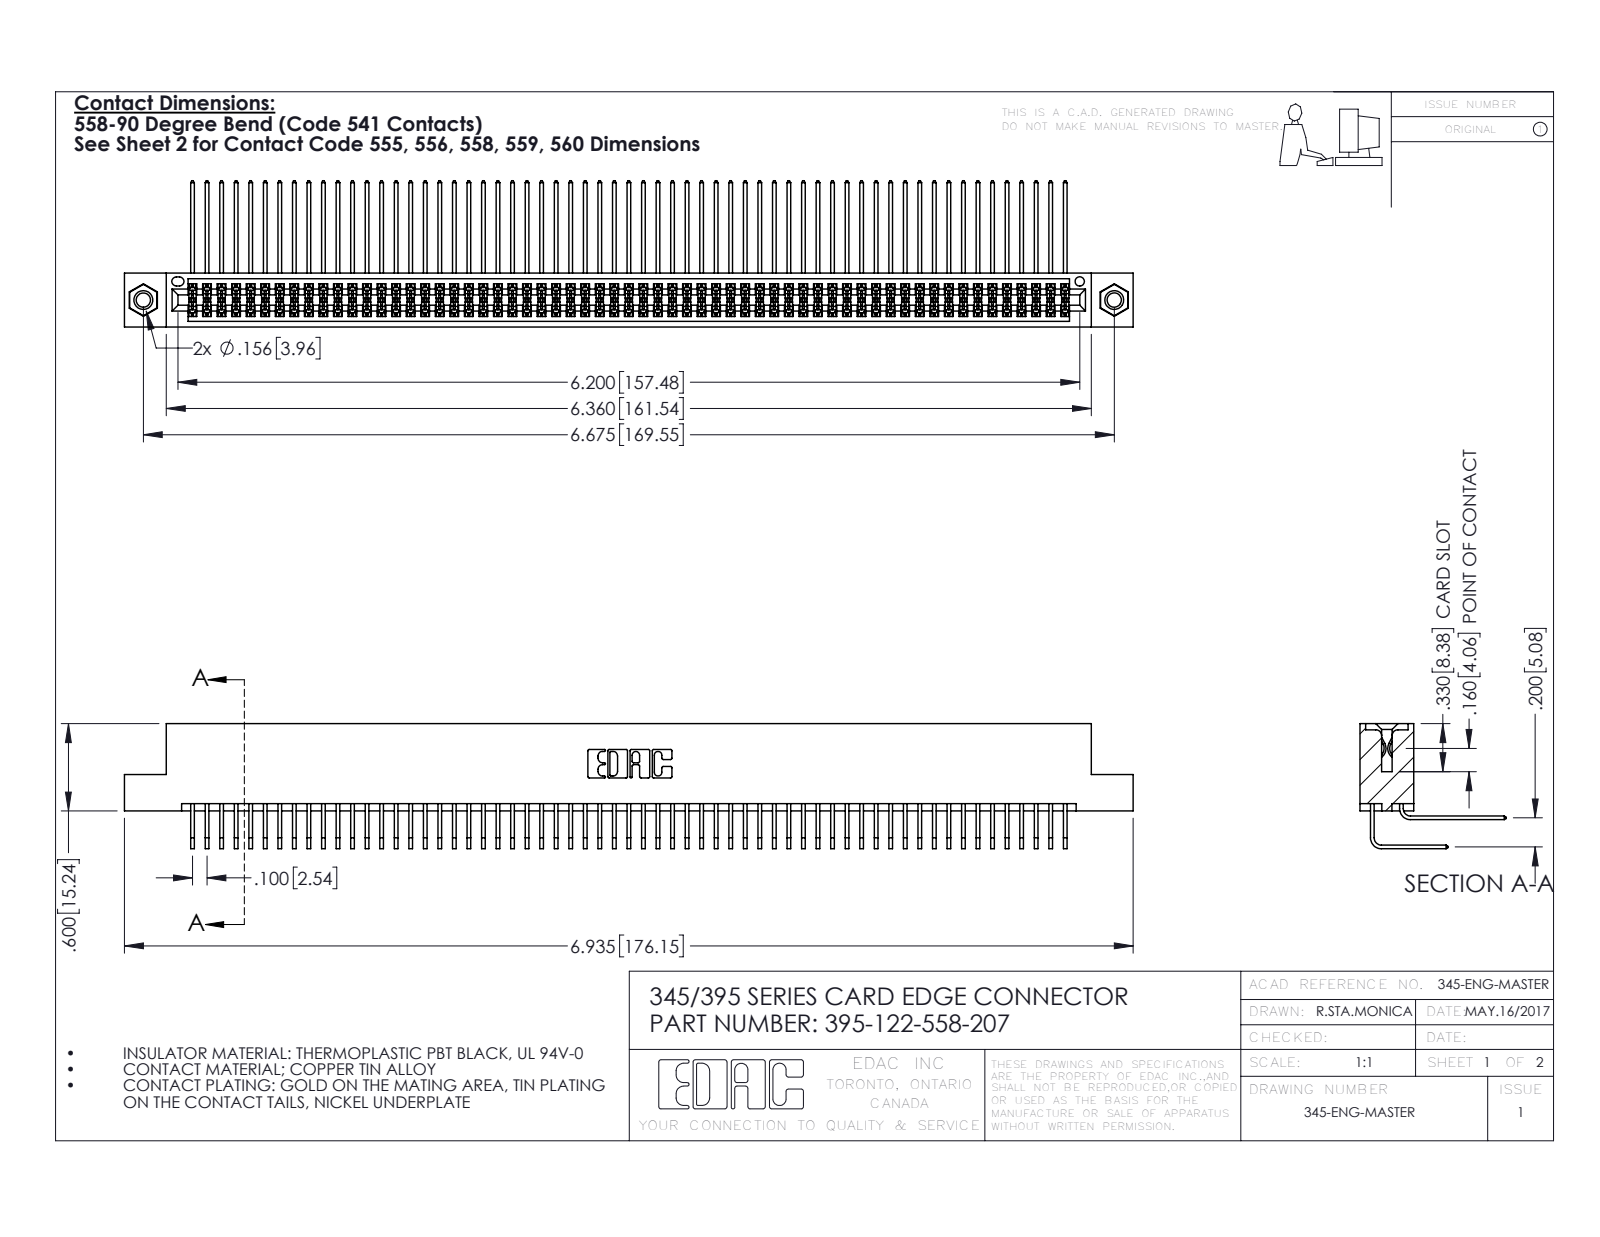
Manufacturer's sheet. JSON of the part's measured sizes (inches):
{"part_name": "345-250-001_345-250-005-103; 345-292-001_558 559 Tail - 1; 345-292-001_558 Tail - 2; 345 Part_Flush Mounting Lugs - 0.156 Dia-TI (+1 more)", "step_written_by": "SolidWorks 2016 (CONFIG_CONTROL_DESIGN)", "units": "inches", "bodies": {"solids": 125, "faces": 6530, "planar": 4382, "cylindrical": 2132, "other": 16}, "overall_size": [6.935, 1.005, 0.859], "volume_in3": 1.097, "surface_area_in2": 46.93, "round_holes": [[0.098, 2], [0.125, 2], [0.156, 2], [0.064, 1]], "round_bosses_or_shafts": [[0.155, 2]], "partial_cylinders_radius": [[0.006, 183], [0.01, 22], [0.007, 6], [0.031, 6], [0.026, 3], [0.014, 2], [0.019, 2], [0.022, 2]], "face_to_face_distances": [0.072, 0.298, 0.2, 0.37, 0.098, 0.272, 0.025, 0.225, 0.025, 0.175], "hole_center_spacings": [0.27, 6.439, 6.675]}
